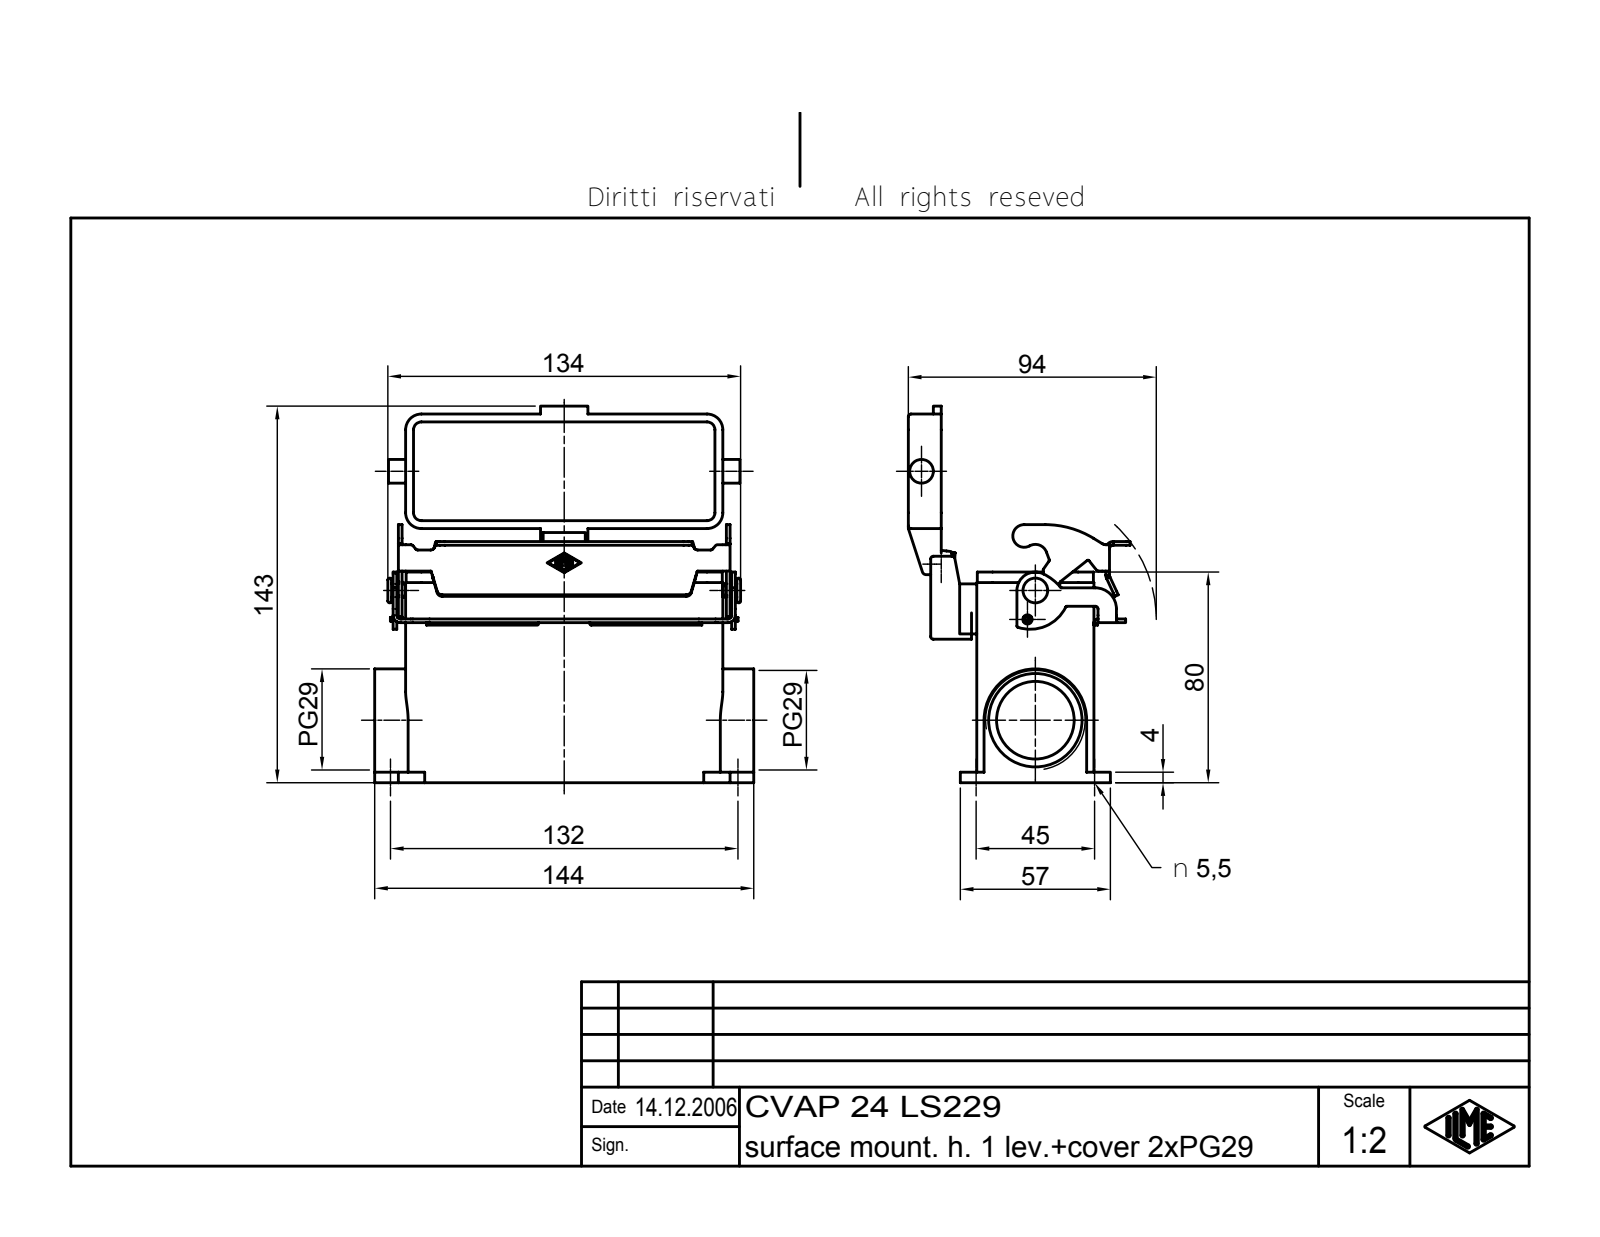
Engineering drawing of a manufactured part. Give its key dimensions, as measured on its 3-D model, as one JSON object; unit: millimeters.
{"part_name": "CVAP 24 LS229", "step_written_by": "Autodesk Inventor 7 (AUTOMOTIVE_DESIGN)", "units": "millimeters", "bodies": {"solids": 4, "faces": 574, "planar": 222, "cylindrical": 187, "other": 165}, "overall_size": [144, 143, 84.23], "volume_mm3": 183645, "surface_area_mm2": 103744, "round_holes": [[5.5, 4], [3.5, 1], [4, 1], [29.48, 1], [35.48, 1]], "round_bosses_or_shafts": [[5, 2], [9, 1], [7, 1], [3.2, 1], [3, 1]], "partial_cylinders_radius": [[1, 27], [0.25, 15], [0.5, 10], [1.5, 10], [6, 8], [2, 7], [1.4, 6], [2.8, 6]], "face_to_face_distances": [4, 40.5, 44.5, 36.5, 30, 23.5, 26, 70.5, 66.5, 64], "hole_center_spacings": [45, 132, 139.46, 38.38]}
